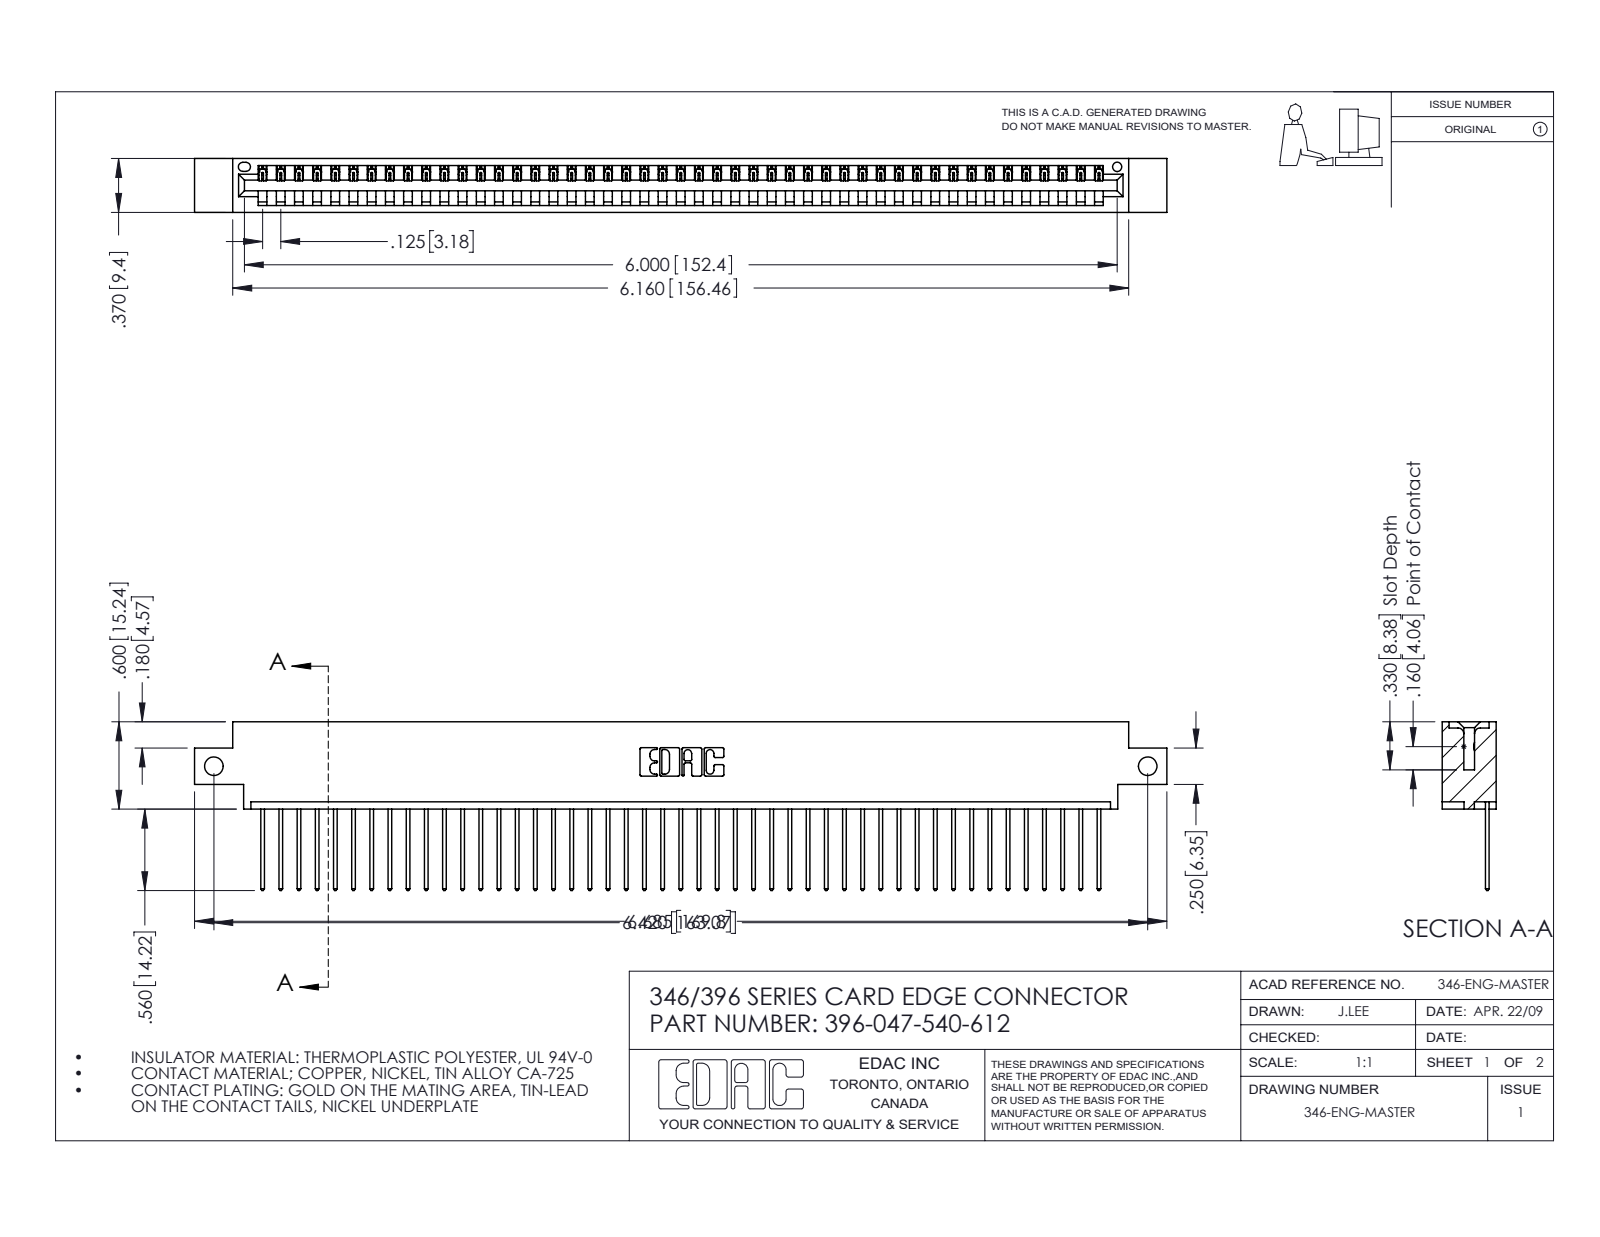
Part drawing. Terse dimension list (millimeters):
name: 396-047-540-612; 346 Part_0.170 Offset - Side Mount; 345-292-001_345-293-140
written by: SolidWorks 2016 (CONFIG_CONTROL_DESIGN)
unit: mm
bodies: 48 solids, 2852 faces (1960 planar, 892 cylindrical, 0 other)
size: 169.8 × 29.5 × 9.4
volume: 16 100 mm³; area: 20 670 mm²
holes: 2× ⌀3.3, 1× ⌀1.6
rounds: 94× R0.2, 94× R0.3, 22× R0.3, 6× R0.2, 6× R0.8, 3× R0.7, 2× R0.8, 2× R1
face distances: 1.2, 8.2, 9.4, 6.4, 1.8, 7.6, 0.6, 3.8, 5.6, 2.5
hole spacings: 163.1
